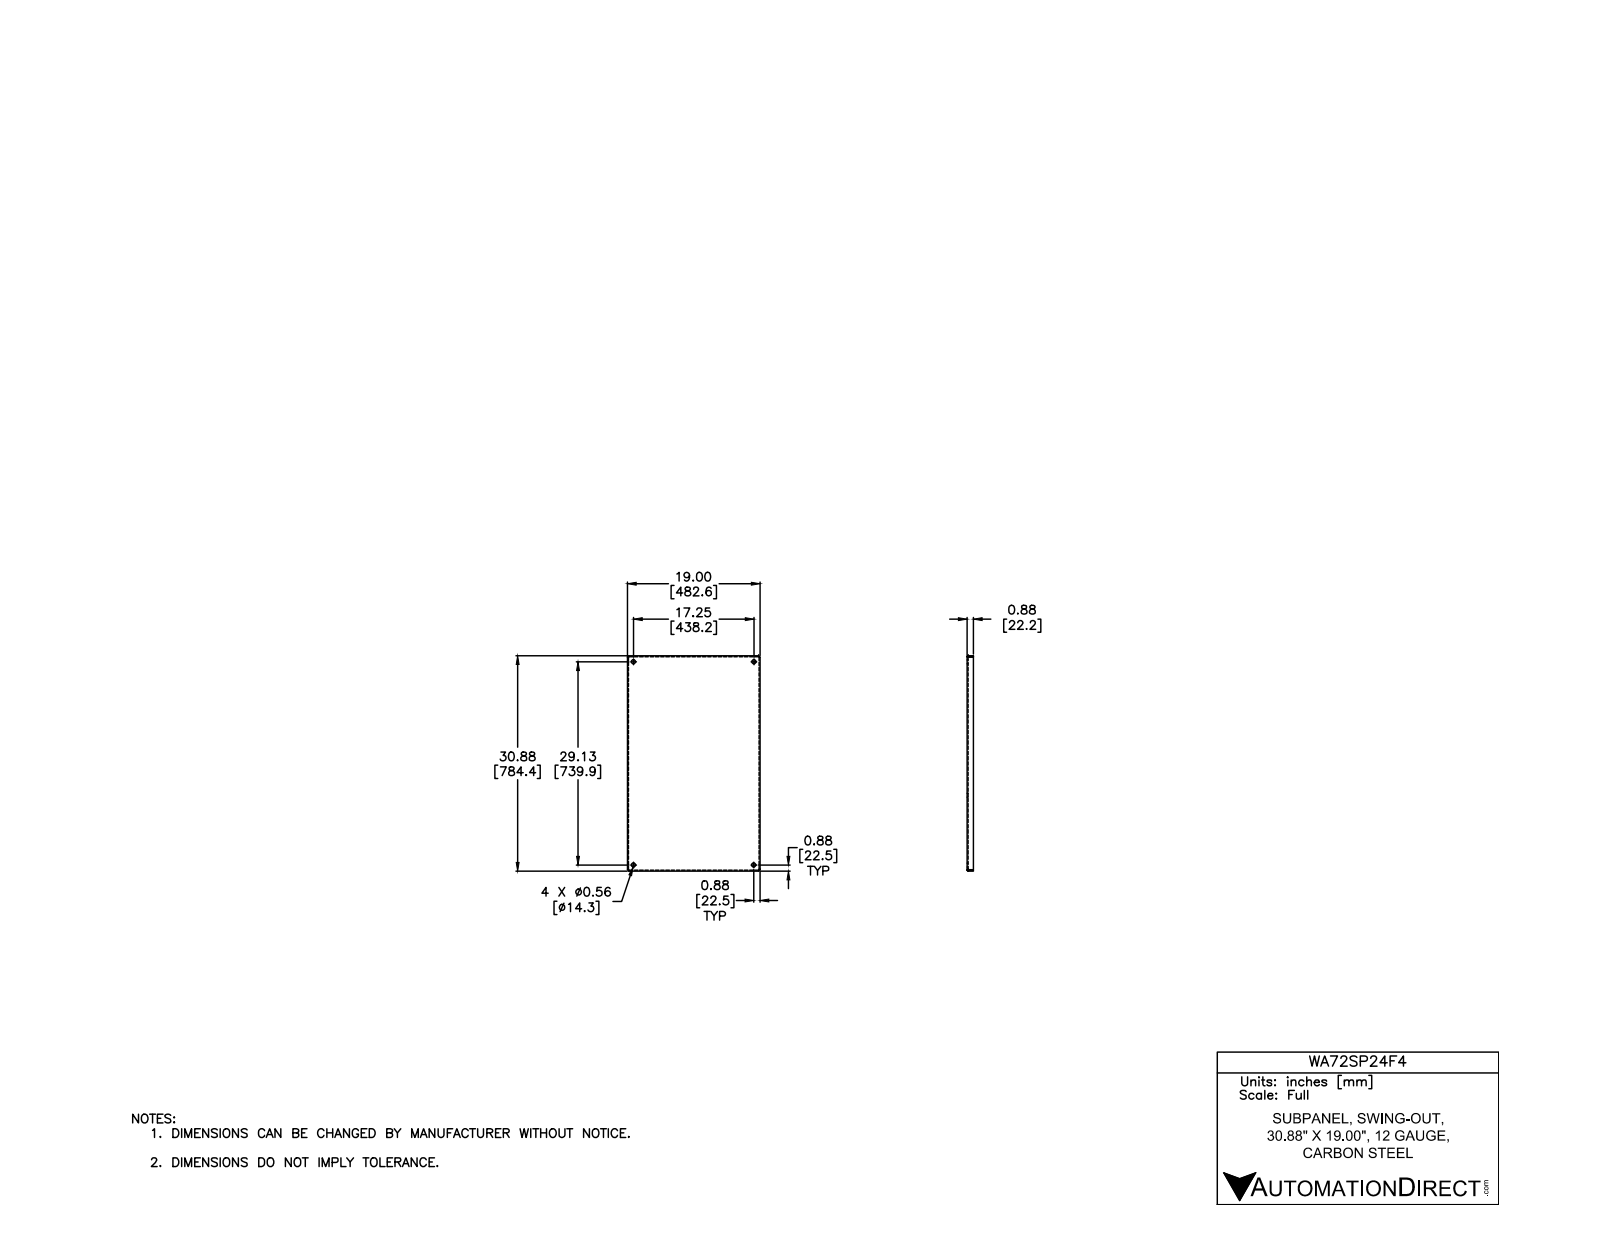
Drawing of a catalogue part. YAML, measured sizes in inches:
part_name: "WA60SP24F3-WA90SP36F4"
step_written_by: "Autodesk Inventor 2012 (AUTOMOTIVE_DESIGN)"
units: inches
bodies: {solids: 1, faces: 42, planar: 22, cylindrical: 12, other: 8}
overall_size: [30.88, 19, 0.875]
volume: 61.81
surface_area: 1329
round_holes:
  - {diameter: 0.563, count: 4}
partial_cylinders:
  - {radius: 0.031, count: 4}
  - {radius: 0.125, count: 4}
face_to_face_distances: [0.094, 18.906, 30.786, 18.813, 19, 30.693, 30.88, 0.781, 0.875, 0.16]
hole_center_spacings: [17.25, 29.13, 33.855]
